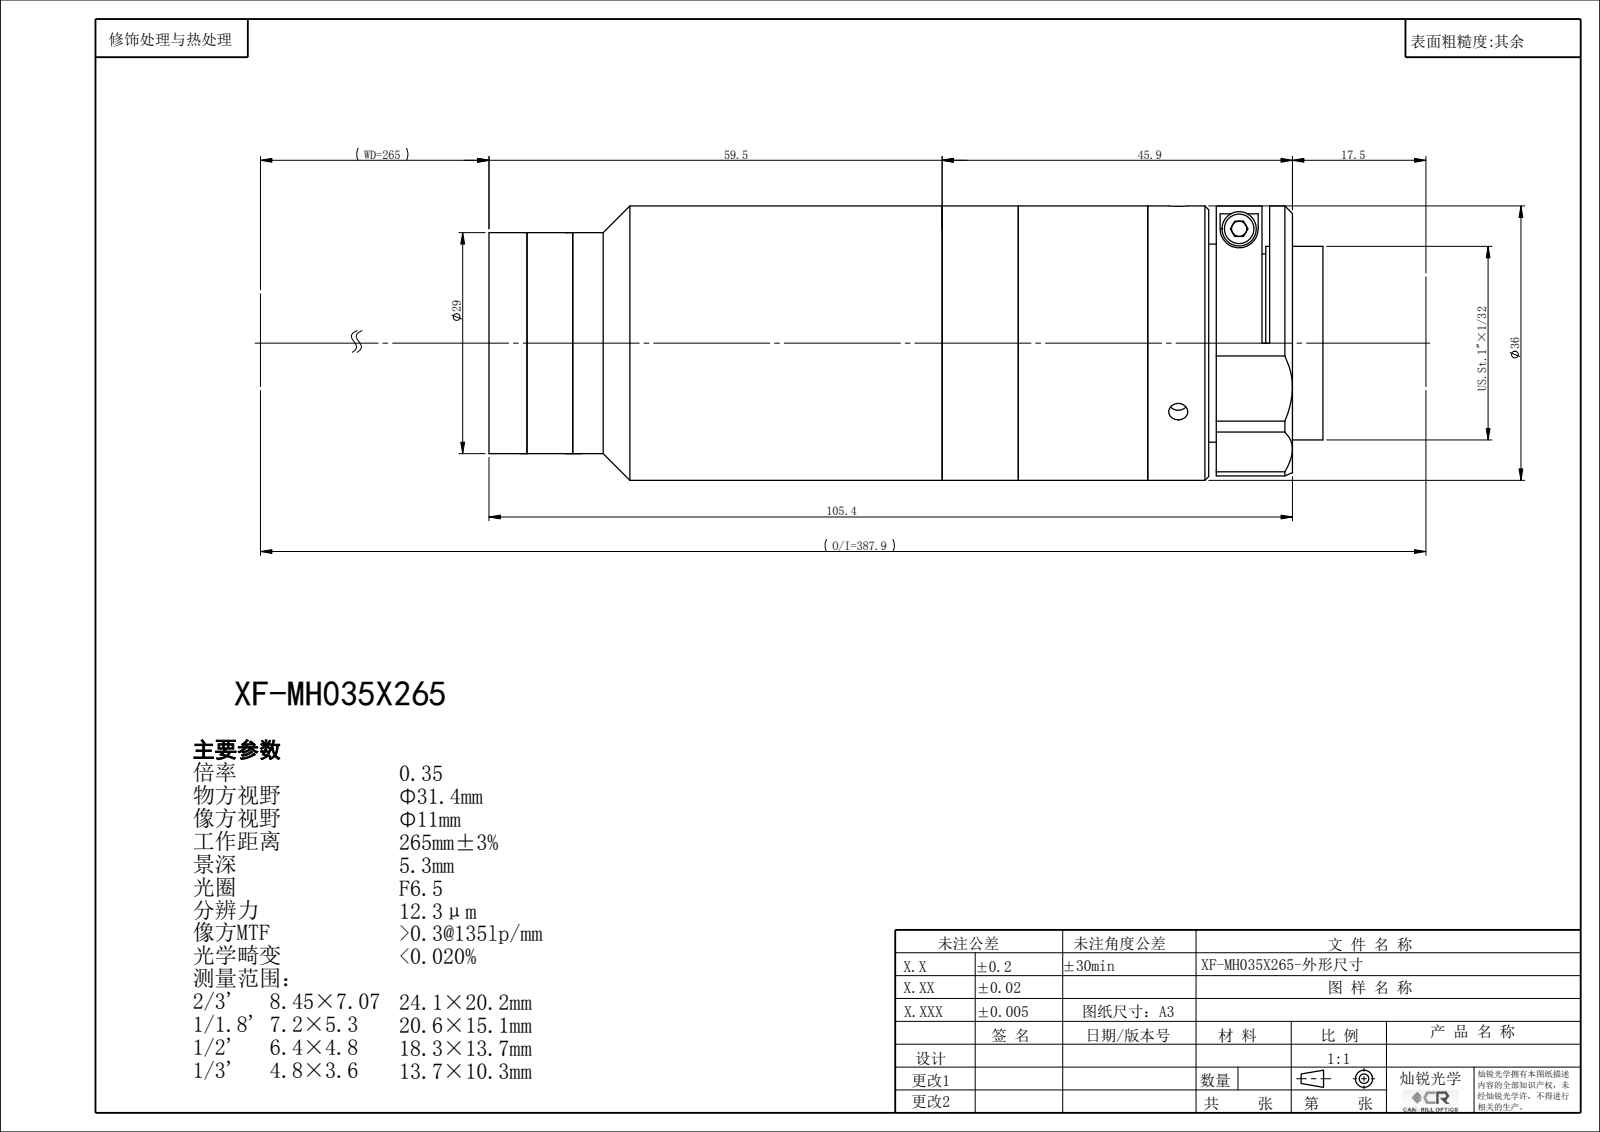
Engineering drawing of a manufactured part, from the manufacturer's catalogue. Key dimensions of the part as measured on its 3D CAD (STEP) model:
Part name (STEP PRODUCT): XF-MH035X265
STEP written by: SolidWorks 2022 (CONFIG_CONTROL_DESIGN)
Units: millimetres
Bodies: 0 solids, 125 faces (61 planar, 42 cylindrical, 22 other)
Overall size (bounding box): 109.35 × 36 × 36
Round holes (diameter × count): ⌀2.5 ×3, ⌀18 ×1, ⌀22.4 ×1, ⌀24 ×1, ⌀24.9 ×1, ⌀26.4 ×1
Round bosses / shafts (diameter × count): ⌀36 ×1, ⌀34 ×1, ⌀29 ×1, ⌀25.4 ×1
Main face-to-face distances: 18.85, 1.5, 17.35, 17, 34.35, 35.85, 10, 27, 44.35, 45.85
